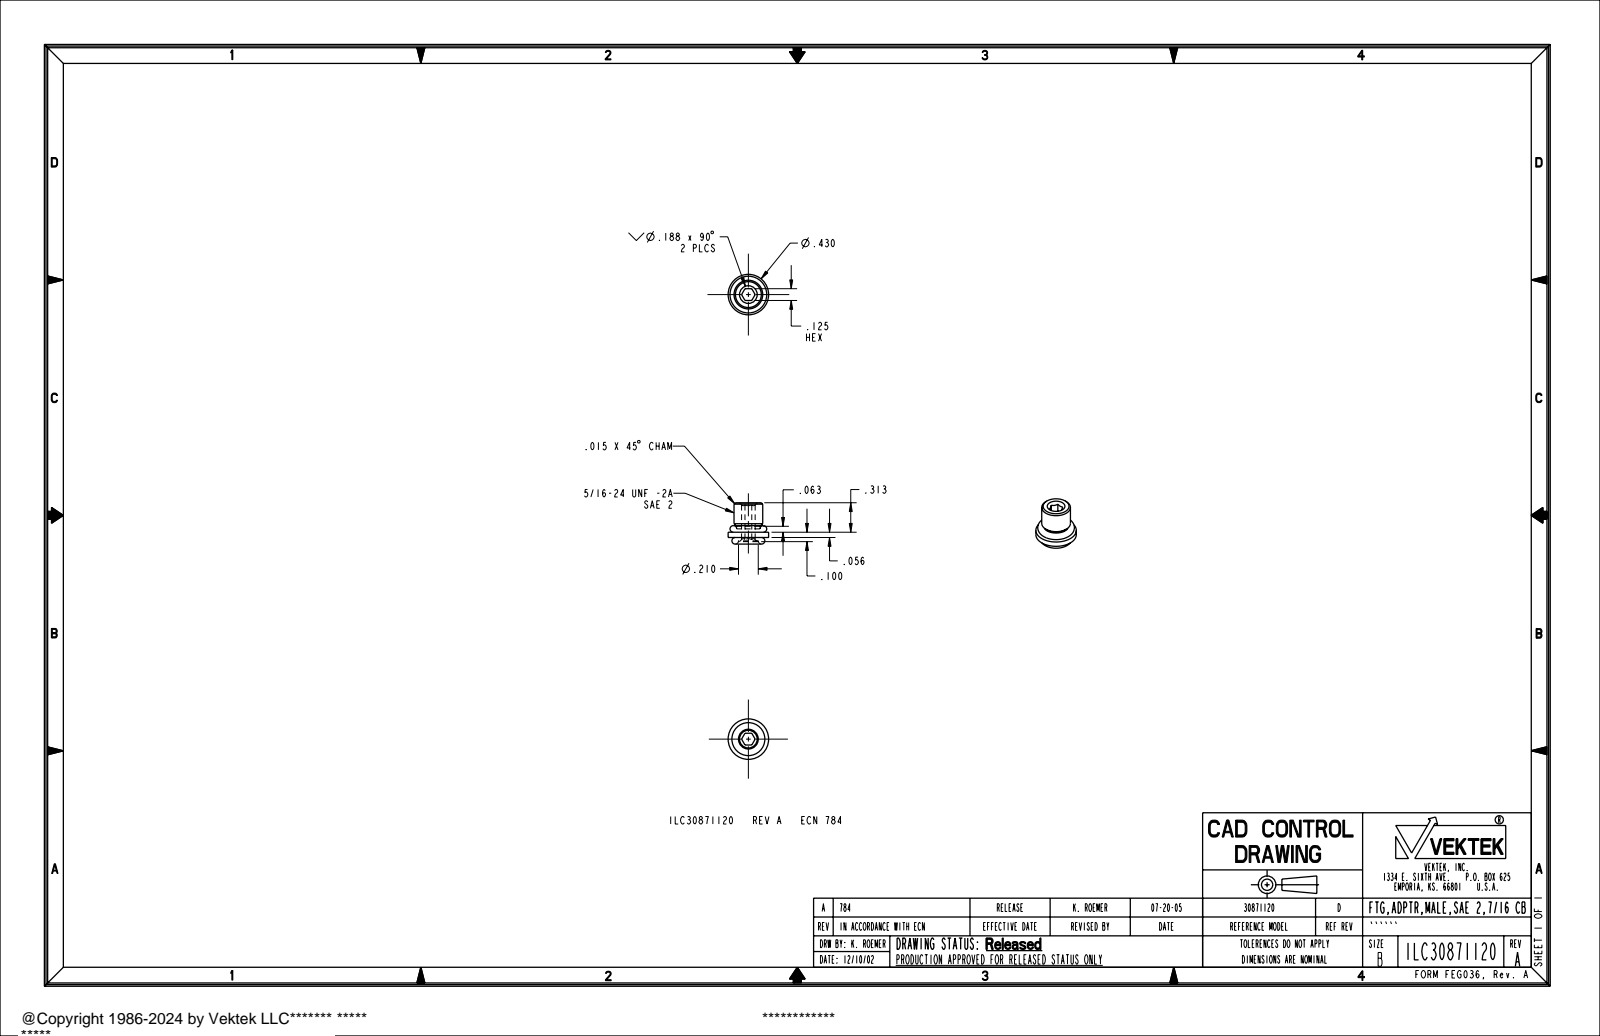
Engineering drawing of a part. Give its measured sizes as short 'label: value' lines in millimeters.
name: ILC30871120
written by: PRO/ENGINEER BY PARAMETRIC TECHNOLOGY CORPORATION, 2004290 (AUTOMOTIVE_DESIGN_CC2)
unit: mm
bodies: 1 solid, 38 faces (10 planar, 8 cylindrical, 20 other)
size: 11.2 × 10.9 × 10.9
volume: 520 mm³; area: 684 mm²
bosses: 1× ⌀10.9, 1× ⌀7.7, 1× ⌀6.4, 1× ⌀5.3
face distances: 3.2, 1.4, 9.4, 8, 1.1, 2.5, 10.5
